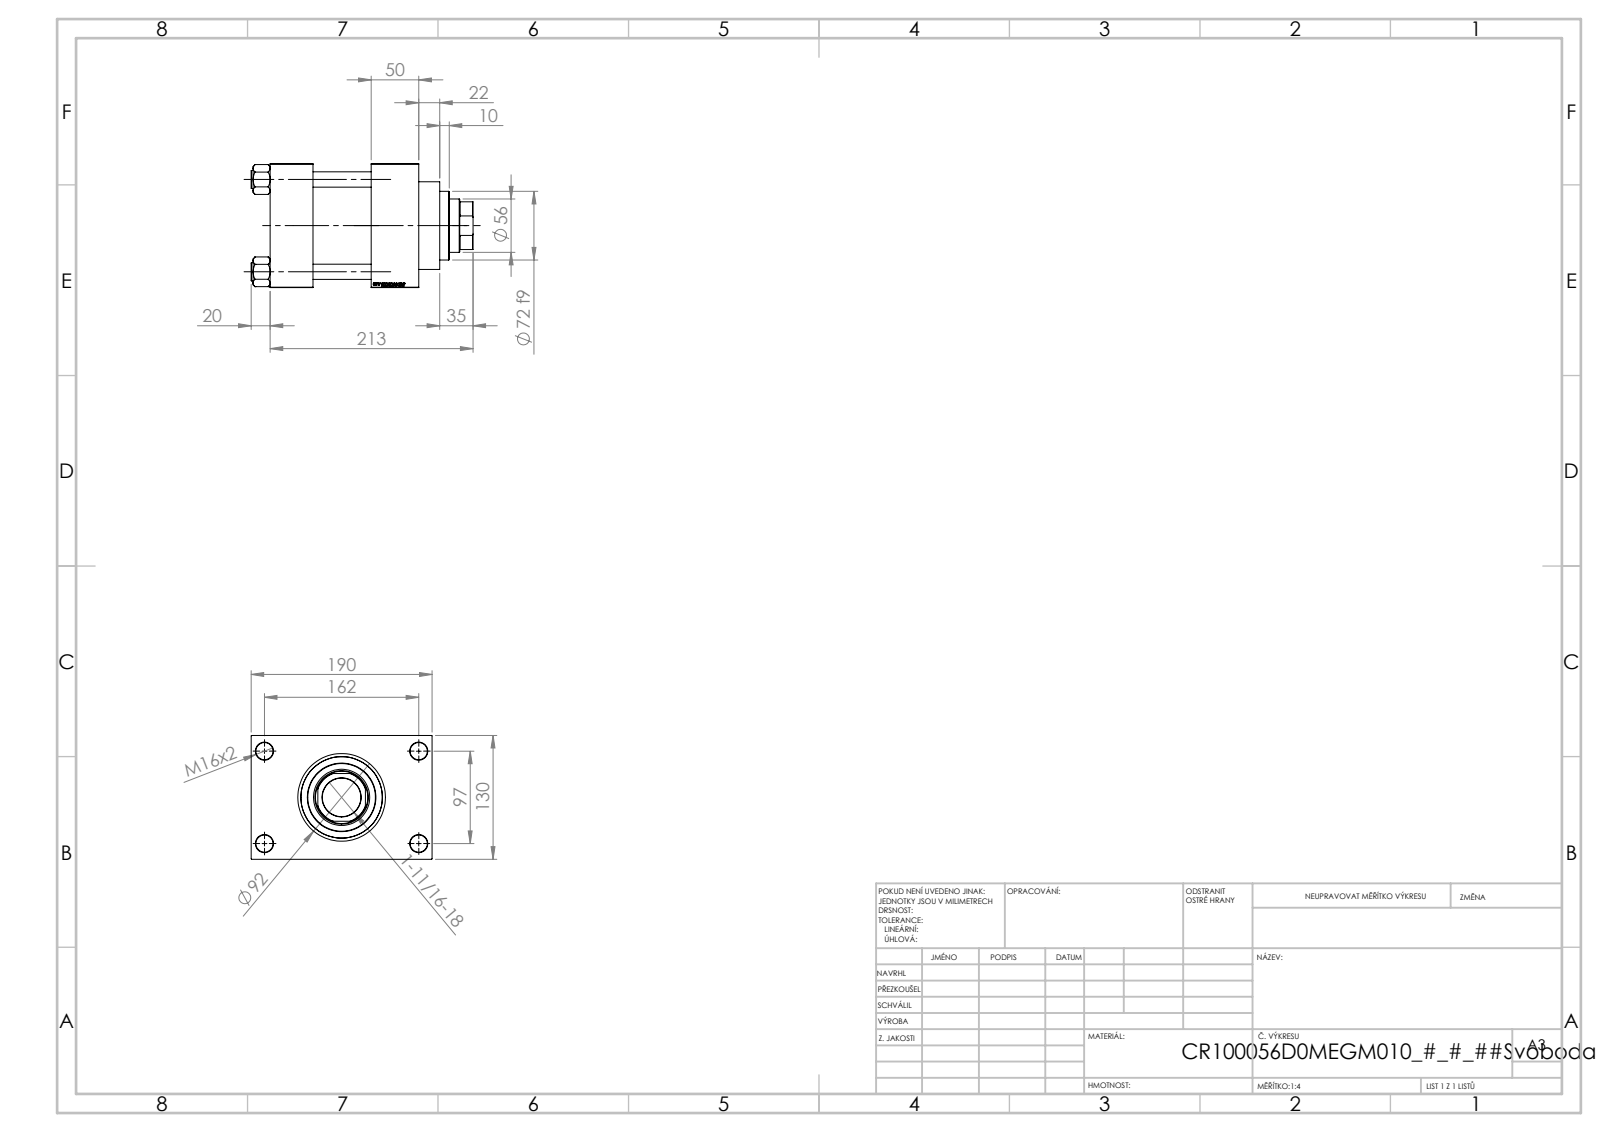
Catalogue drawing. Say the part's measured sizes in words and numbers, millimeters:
The part is named "V215CR_D_TYCINKA; V215CR_VCP_D; NUT_M5_D; V215_VC_A (+1 more)". Its 3-D file was written by "SolidWorks 2019 (CONFIG_CONTROL_DESIGN)". It is 11 solids with 1152 faces: 545 planar, 89 cylindrical and 518 other. Overall it measures 233 by 190 by 130 millimeters. Its volume is 2 602 000 cubic millimeters and its surface area 349 632 square millimeters. Round holes: 4 of diameter 16, 4 of diameter 18, 2 of diameter 7, 2 of diameter 26.44, 2 of diameter 35, 1 of diameter 40.5, 1 of diameter 56, 1 of diameter 59, 1 of diameter 76, 1 of diameter 85.5, 1 of diameter 100. Round bosses or shafts: 4 of diameter 19, 1 of diameter 106, 1 of diameter 92, 1 of diameter 72. Partial cylindrical surfaces (rounded edges, fillets, slot ends): 1 of radius 27. The main face-to-face distances are 130, 50, 45, 106, 61, 156, 111, 30, 160, 10. The hole center spacings are 32.55, 68.52, 94.41, 96.9, 102.27, 129.45, 161.73, 97.
